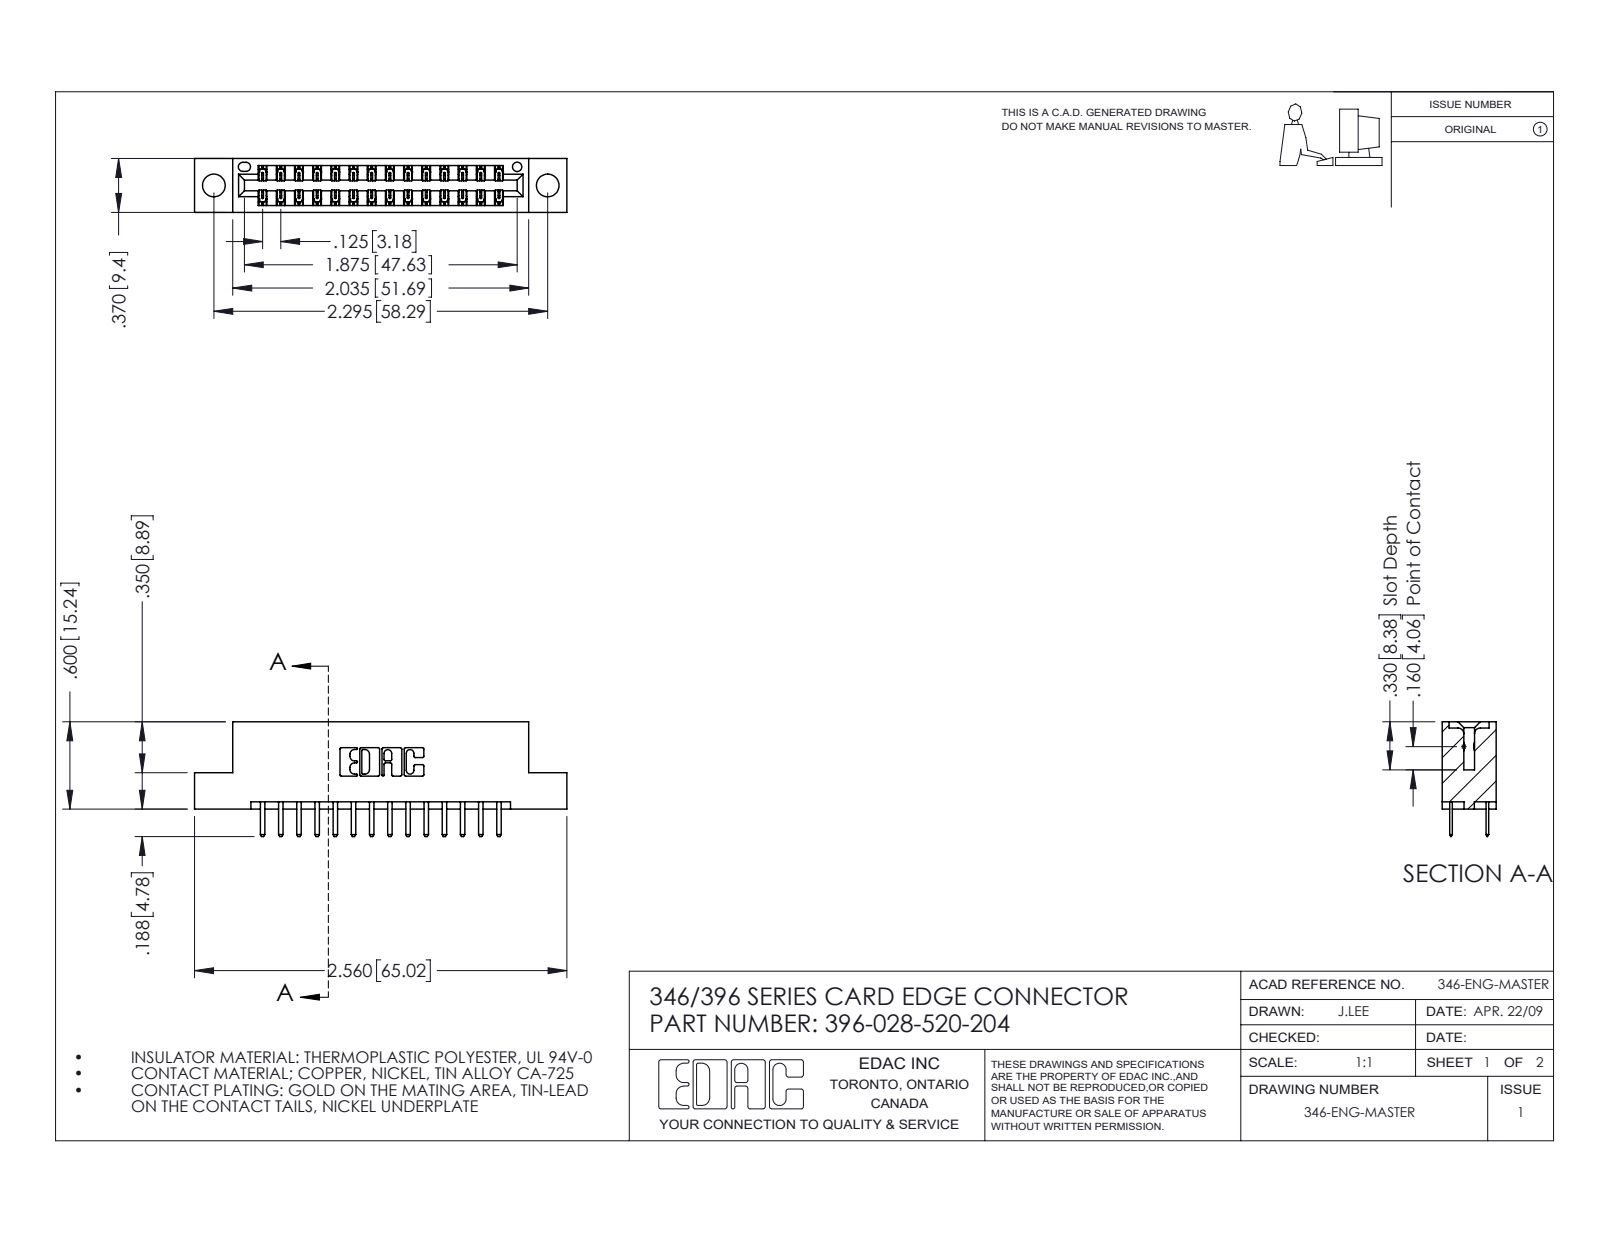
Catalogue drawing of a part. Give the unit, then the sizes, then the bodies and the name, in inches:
Units: inches
Overall size (bounding box): 2.56 × 0.788 × 0.37
Round holes (diameter × count): ⌀0.156 ×2, ⌀0.064 ×1
Partial cylindrical surfaces — rounded edges, fillets, slot ends (radius × count): R0.006 ×42, R0.01 ×32, R0.01 ×22, R0.007 ×6, R0.031 ×6, R0.026 ×3, R0.014 ×2, R0.022 ×2
Main face-to-face distances: 0.25, 0.048, 0.322, 0.37, 0.275, 0.072, 0.298, 0.025, 0.148, 0.222
Hole centre spacings: 0.246, 2.089, 2.295
Volume: 0.368 in³ · Surface area: 11.82 in²
Bodies: 29 solids, 1690 faces (1112 planar, 578 cylindrical, 0 other)
Part name (STEP PRODUCT): 345-292-001_345-293-120; 396-028-520-204; 346 Part_Flush Mounting Lugs - 0.156 Dia-TH
STEP written by: SolidWorks 2016 (CONFIG_CONTROL_DESIGN)
